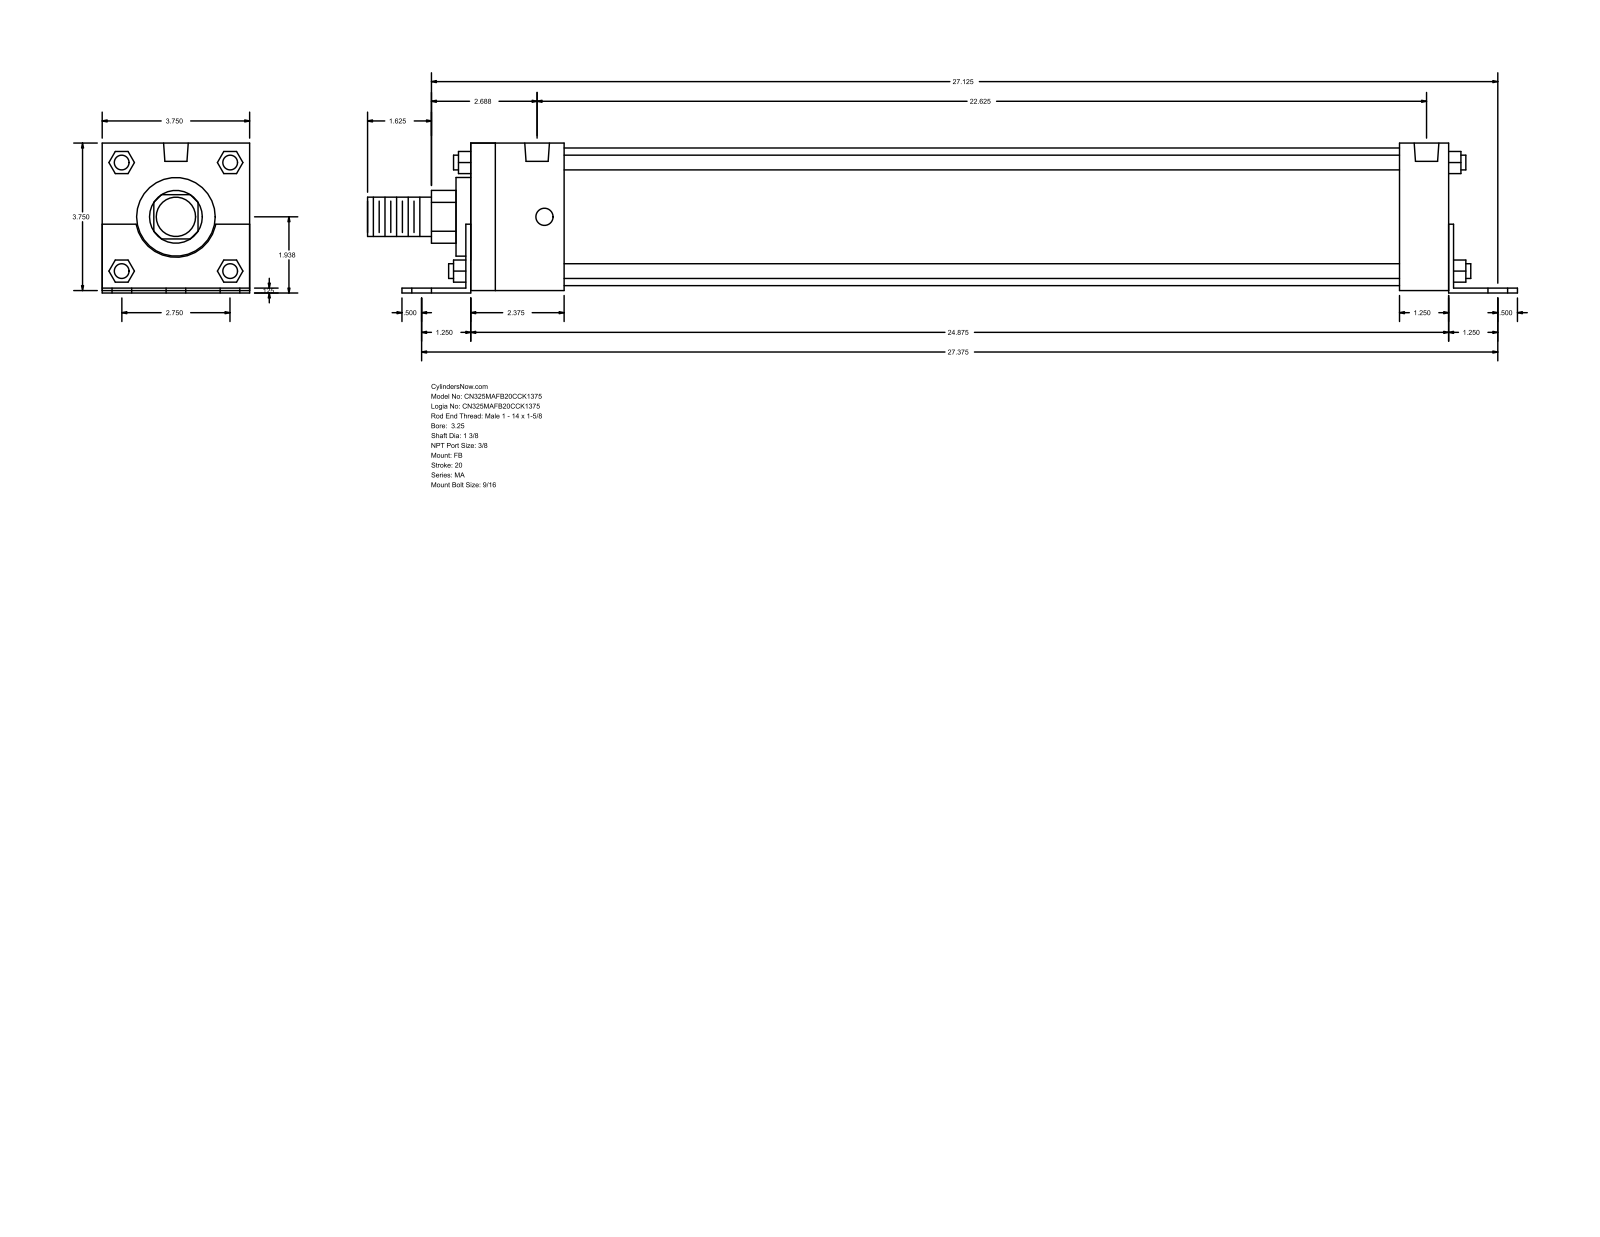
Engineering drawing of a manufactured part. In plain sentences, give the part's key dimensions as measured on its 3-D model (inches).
The part is named "MA_FB__0325_1.375". Its 3-D file was written by "GSSL Pune (CONFIG_CONTROL_DESIGN)". It is 0 solids with 140 faces: 105 planar, 35 cylindrical and 0 other. Overall it measures 29.25 by 3.813 by 3.75 inches. Round holes: 6 of diameter 0.563, 4 of diameter 0.437, 2 of diameter 0.627. Round bosses or shafts: 4 of diameter 0.375, 1 of diameter 3.5, 1 of diameter 2, 1 of diameter 1.375, 1 of diameter 1. Partial cylindrical surfaces (rounded edges, fillets, slot ends): 1 of radius 0.672, 1 of radius 1.03. The main face-to-face distances are 3.75, 0.125, 0.063, 3.812, 0.062, 3.687, 25, 24.875, 1.25, 1.375. The hole center spacings are 1.375, 27.41, 27.375, 0.188, 2.275, 2.427, 2.75, 3.243.
